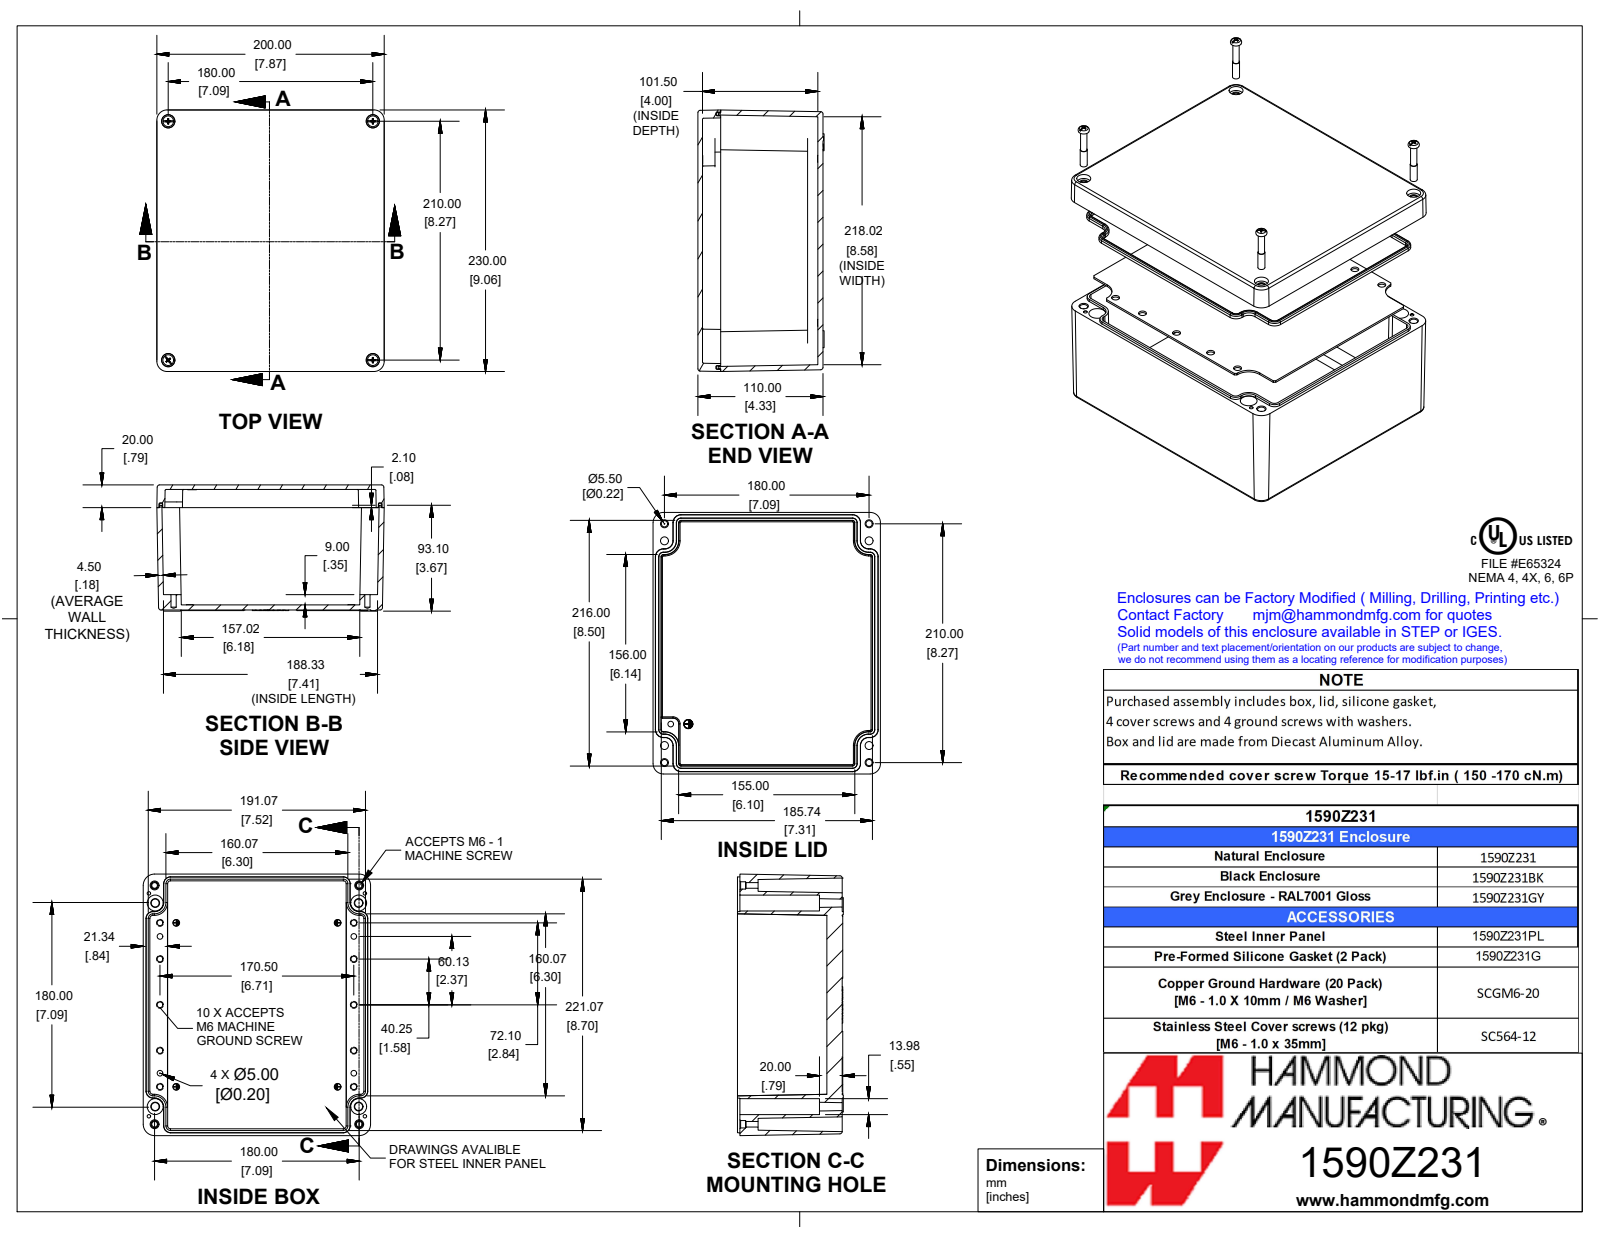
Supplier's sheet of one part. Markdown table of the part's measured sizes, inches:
| quantity | value |
| --- | --- |
| part name | 1590Z231GY |
| STEP written by | SolidWorks 2019 (CONFIG_CONTROL_DESIGN) |
| units | inches |
| bodies | 7 solids, 1109 faces (576 planar, 128 cylindrical, 405 other) |
| overall size | 9.055 × 7.874 × 4.37 |
| volume | 57.28 in³ |
| surface area | 626.6 in² |
| round holes (diameter × count) | 0.194 × 15, 0.217 × 8, 0.276 × 8, 0.118 × 4, 0.197 × 4, 0.256 × 4, 0.551 × 4 |
| round bosses / shafts (diameter × count) | 0.235 × 4, 0.231 × 4, 0.208 × 4 |
| partial cylindrical surfaces (radius × count) | 0.039 × 26, 0.02 × 16, 0.057 × 8, 0.079 × 8 |
| main face-to-face distances | 0.177, 4.331, 0.157, 4.173, 3.996, 4.154, 0.787, 0.61, 0.63, 0.276 |
| hole center spacings | 6.713, 0.339, 0.398, 0.472, 0.561, 0.611, 0.705, 0.733 |
